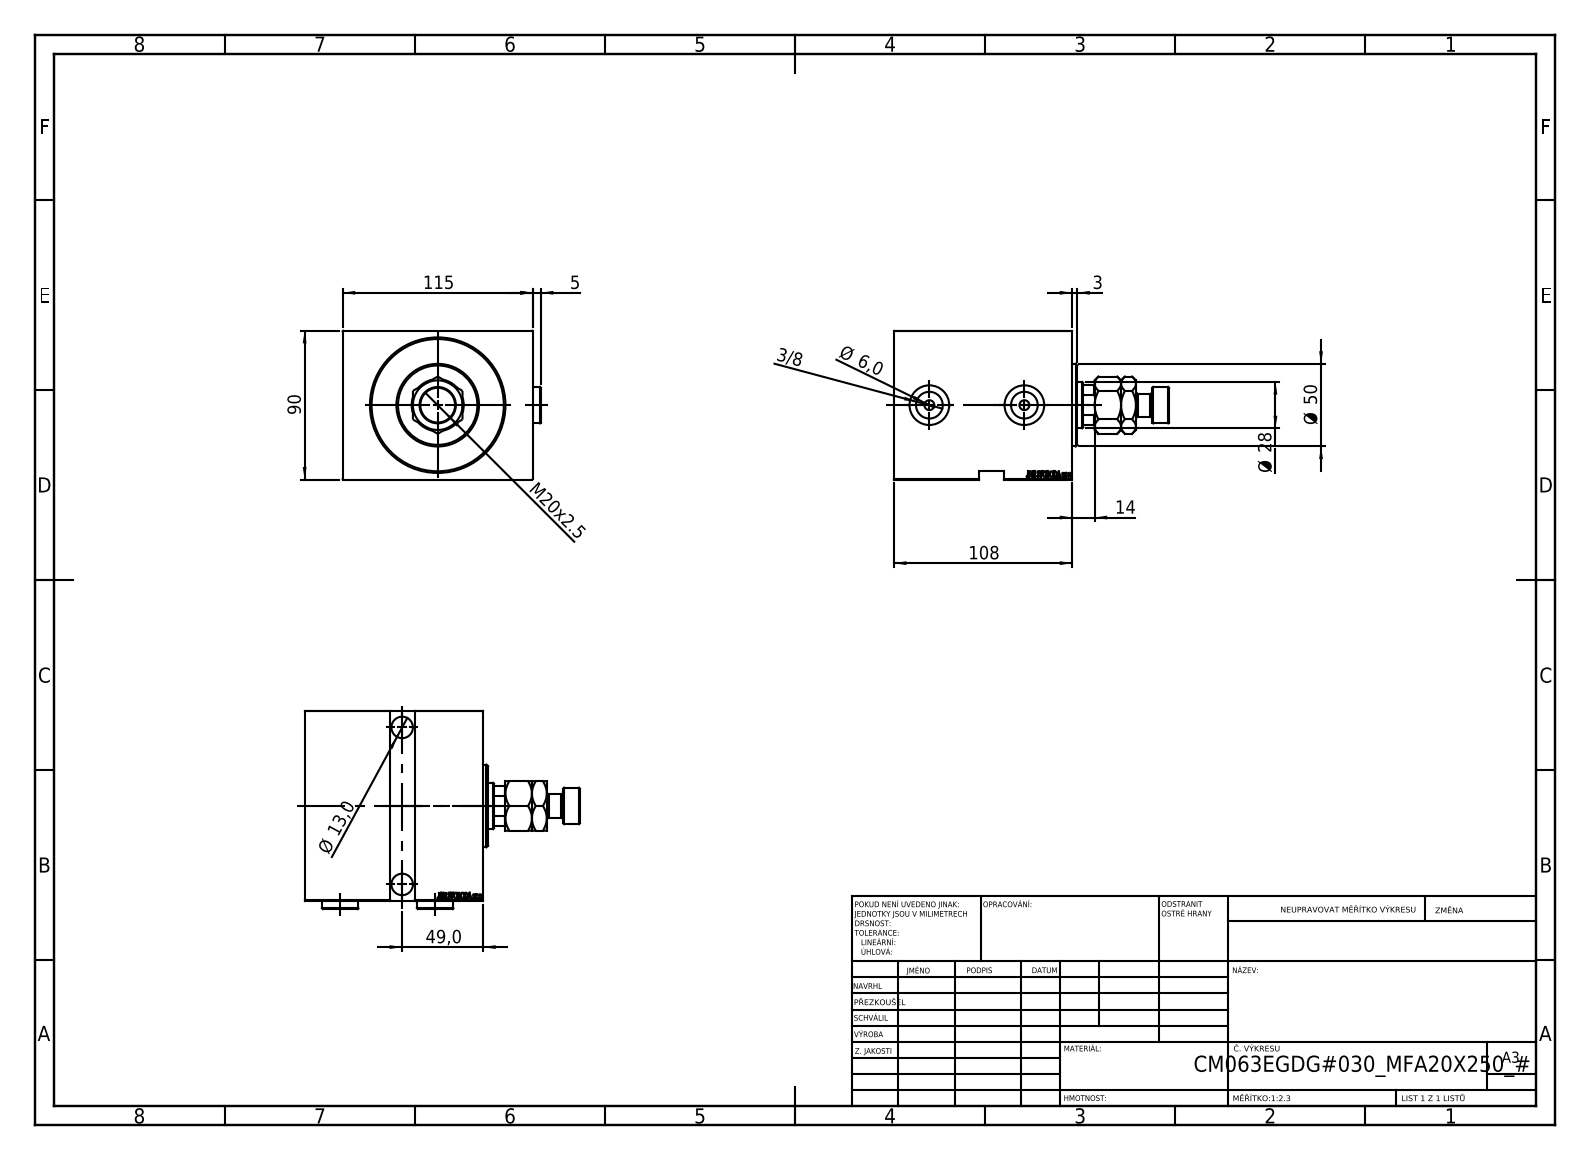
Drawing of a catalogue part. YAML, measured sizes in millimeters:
part_name: "V450CM_E_Body; V450CM_E_VCP; MFA; V450CM_VC_B (+1 more)"
step_written_by: "SolidWorks 2019 (CONFIG_CONTROL_DESIGN)"
units: millimeters
bodies: {solids: 6, faces: 954, planar: 460, cylindrical: 64, other: 430}
overall_size: [166.5, 119.9, 90]
volume: 1034000
surface_area: 139182
round_holes:
  - {diameter: 6, count: 2}
  - {diameter: 13, count: 2}
  - {diameter: 16.17, count: 2}
  - {diameter: 19, count: 2}
  - {diameter: 24, count: 2}
  - {diameter: 18.5, count: 1}
  - {diameter: 28, count: 1}
  - {diameter: 31.5, count: 1}
  - {diameter: 63, count: 1}
  - {diameter: 80, count: 1}
round_bosses_or_shafts:
  - {diameter: 22, count: 3}
  - {diameter: 65, count: 1}
  - {diameter: 50, count: 1}
  - {diameter: 14, count: 1}
partial_cylinders:
  - {radius: 13.5, count: 1}
face_to_face_distances: [90, 115, 108, 17.5, 90.5, 5, 103, 85.5, 38.5, 43.5]
hole_center_spacings: [57.5, 95]
